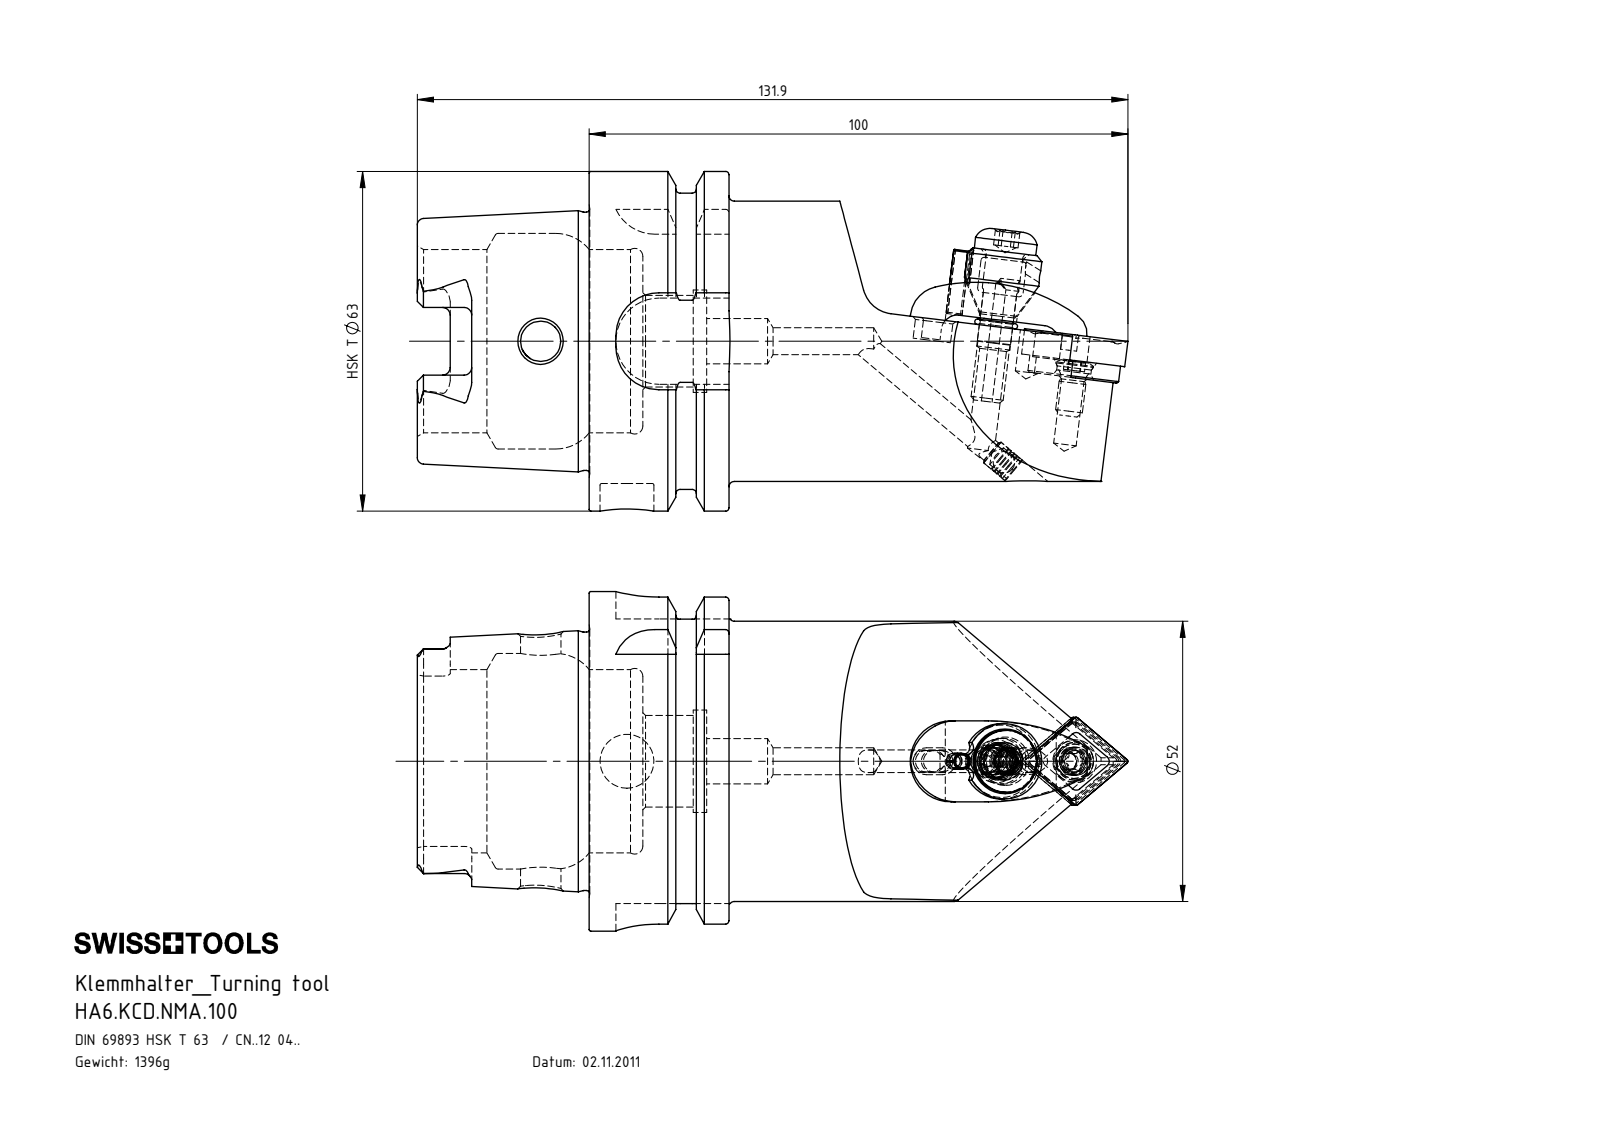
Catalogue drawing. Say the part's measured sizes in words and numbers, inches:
The part is named "WCC-ER3.102.024_C; KVT_MB_600_050; WCC-ER2.001.010_A; WCC-ER4.103.032_A (+7 more)". Its 3-D file was written by "SolidWorks 2017 (AUTOMOTIVE_DESIGN)". It is 11 solids with 466 faces: 125 planar, 152 cylindrical and 189 other. Overall it measures 5.193 by 2.48 by 2.48 inches. Its volume is 10.8 cubic inches and its surface area 57.56 square inches. Round holes: 3 of diameter 0.079, 3 of diameter 0.165, 3 of diameter 0.197, 2 of diameter 0.276, 1 of diameter 0.094, 1 of diameter 0.118, 1 of diameter 0.157, 1 of diameter 0.203, 1 of diameter 0.244, 1 of diameter 0.258, 1 of diameter 0.295, 1 of diameter 0.331. Round bosses or shafts: 2 of diameter 0.197, 2 of diameter 0.118, 1 of diameter 2.48, 1 of diameter 2.163, 1 of diameter 2.047, 1 of diameter 1.887, 1 of diameter 0.551, 1 of diameter 0.453. Partial cylindrical surfaces (rounded edges, fillets, slot ends): 6 of radius 0.015, 6 of radius 0.027, 6 of radius 0.055, 4 of radius 0.016, 4 of radius 0.039, 4 of radius 0.315, 3 of radius 0.059, 2 of radius 0.079. The main face-to-face distances are 1.022, 0.63, 0.392, 1.256, 1.648, 2.278, 2.079, 0.858, 0.467, 2.114. The hole center spacings are 0.315, 0.263, 0.323, 0.578, 0.591, 0.605, 0.906, 0.015.
